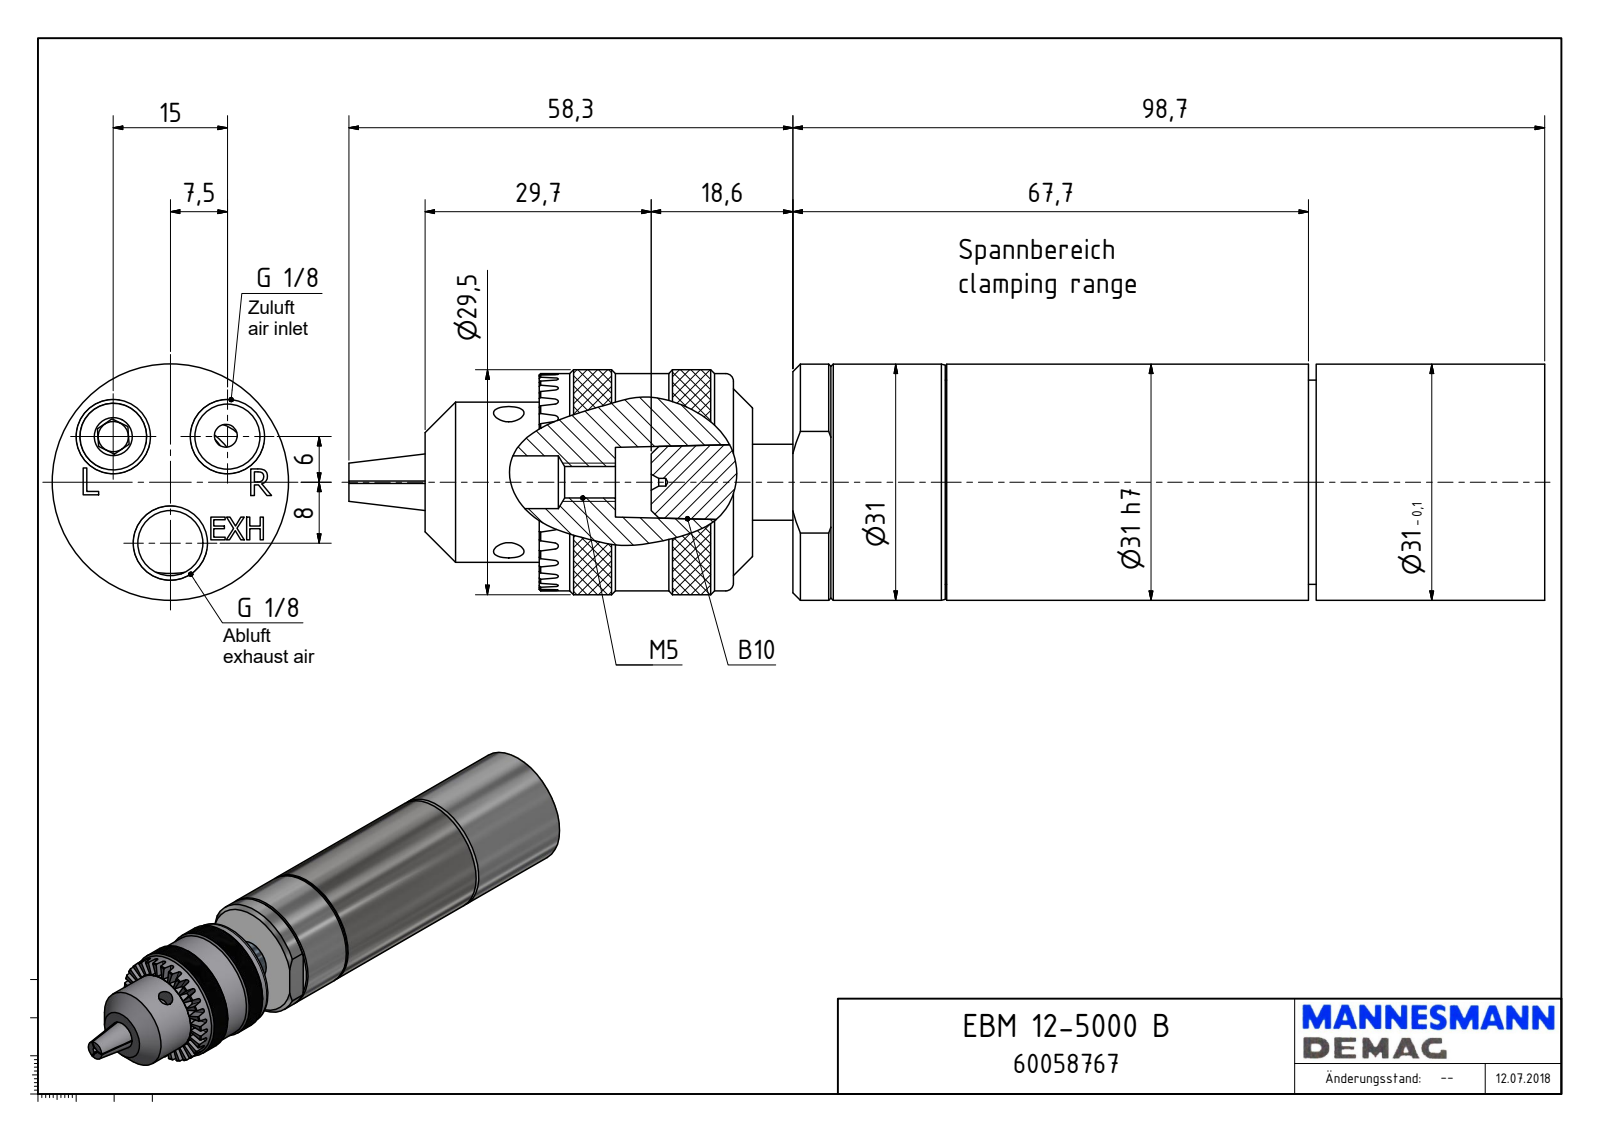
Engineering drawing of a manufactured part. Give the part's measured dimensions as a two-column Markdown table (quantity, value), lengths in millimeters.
| quantity | value |
| --- | --- |
| part name | EBM 12-5000 B_60058767 |
| STEP written by | Autodesk Inventor 2018 (AUTOMOTIVE_DESIGN) |
| units | millimeters |
| bodies | 1 solid, 346 faces (223 planar, 57 cylindrical, 66 other) |
| overall size | 157 × 31 × 31 |
| volume | 94 168 mm³ |
| surface area | 19 188 mm² |
| round holes (diameter × count) | 4 × 4, 8.57 × 3, 1 × 1, 1.5 × 1, 4.13 × 1, 6.9 × 1, 10.5 × 1, 29.3 × 1 |
| round bosses / shafts (diameter × count) | 31 × 1, 29.5 × 1, 28.5 × 1, 26.79 × 1, 21 × 1, 10 × 1 |
| partial cylindrical surfaces (radius × count) | 0.5 × 23 |
| main face-to-face distances | 98.7, 25.5, 28, 5.3, 104, 78.5, 20.2, 73, 67.7, 47.5 |
| hole center spacings | 9.6, 15.88, 8, 15 |
